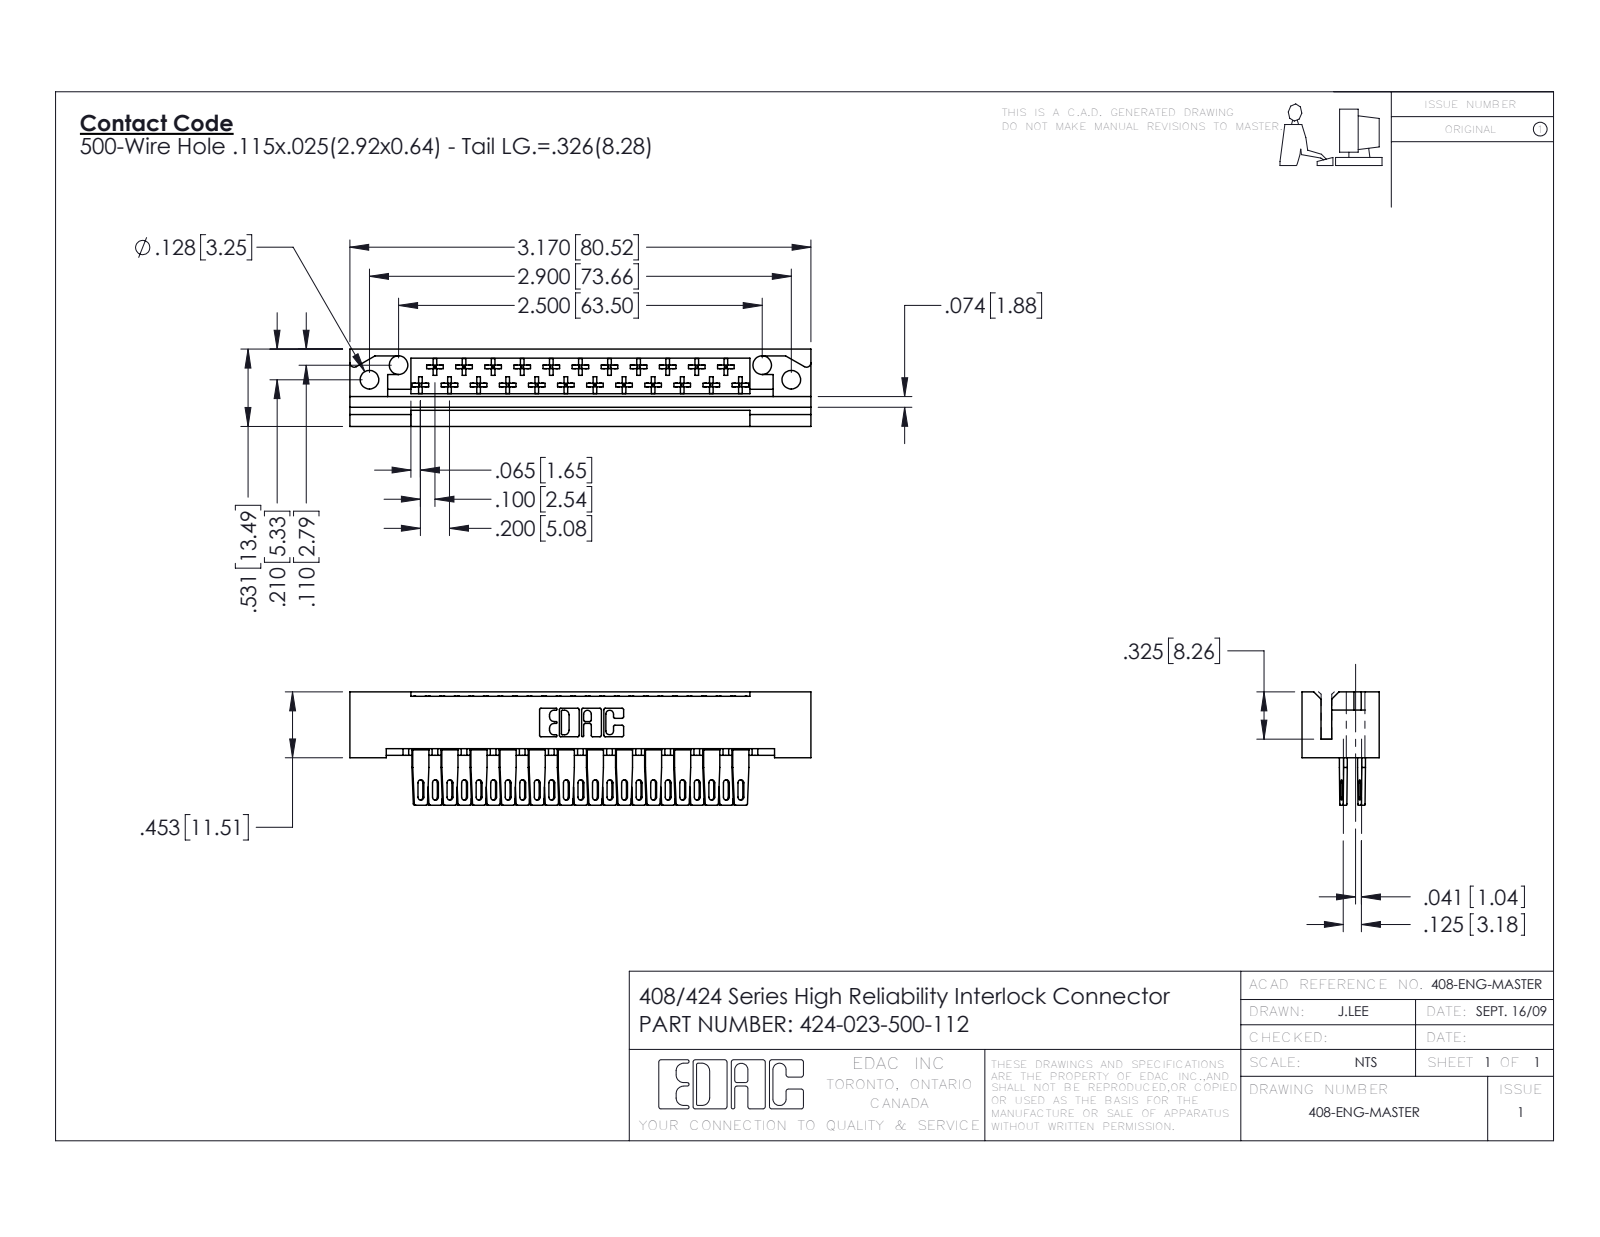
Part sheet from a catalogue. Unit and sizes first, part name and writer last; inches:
Units: inches
Overall size (bounding box): 3.17 × 0.779 × 0.531
Round holes (diameter × count): ⌀0.128 ×4
Partial cylindrical surfaces — rounded edges, fillets, slot ends (radius × count): R0.01 ×184, R0.021 ×46, R0.02 ×25, R0.01 ×22, R0.007 ×6, R0.031 ×6, R0.026 ×3, R0.03 ×2
Main face-to-face distances: 0.4, 0.025, 0.531, 0.125, 0.1, 0.326, 0.131, 0.074, 0.205, 0.091
Hole centre spacings: 0.224, 2.702, 2.5, 2.9
Volume: 0.548 in³ · Surface area: 17.77 in²
Bodies: 24 solids, 1456 faces (1032 planar, 332 cylindrical, 92 other)
Part name (STEP PRODUCT): 408-290-001_408-290-100; 424 Part_023; 424-023-500-112
STEP written by: SolidWorks 2016 (CONFIG_CONTROL_DESIGN)
